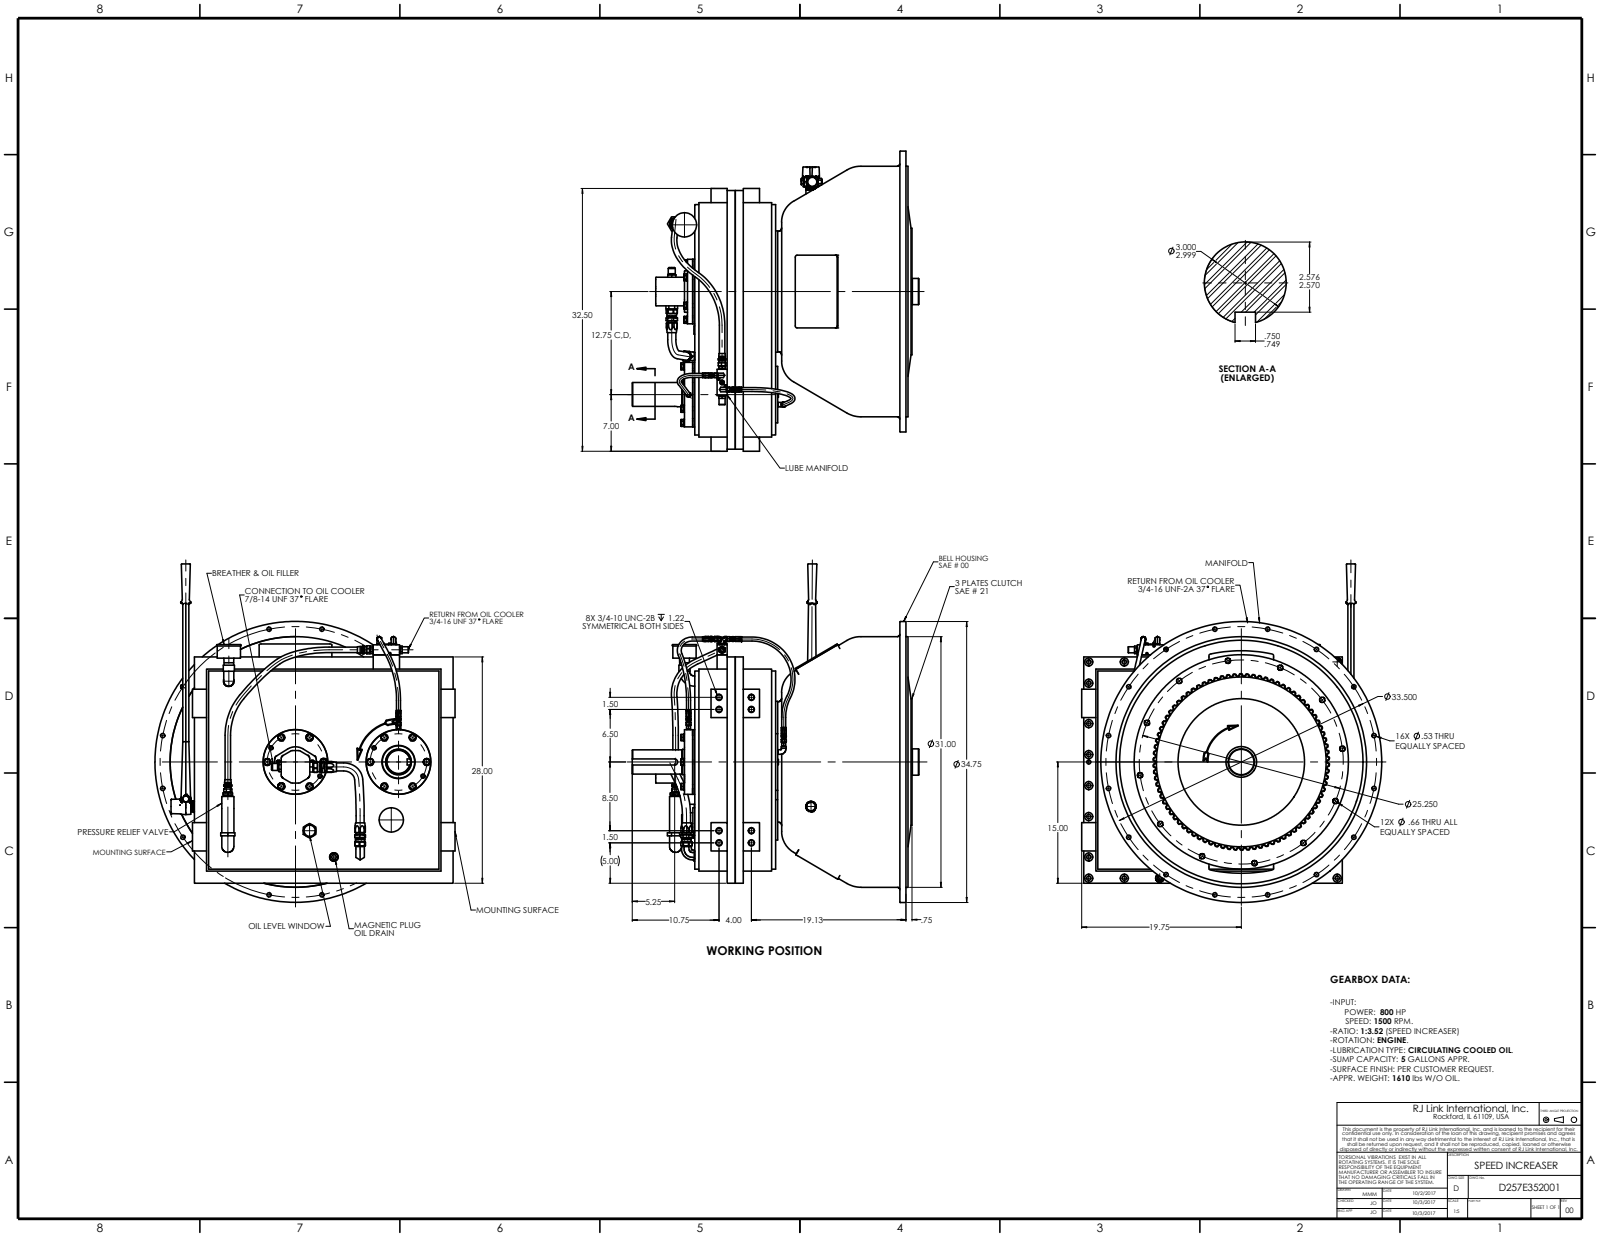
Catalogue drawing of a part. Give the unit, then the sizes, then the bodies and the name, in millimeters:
Units: millimetres
Overall size (bounding box): 1063.7 × 943 × 901.3
Round holes (diameter × count): ⌀13.5 ×70, ⌀25.4 ×34, ⌀16.7 ×20, ⌀12.9 ×12, ⌀16.7 ×12, ⌀5.2 ×6, ⌀6.4 ×6, ⌀16.2 ×6, ⌀11.1 ×5, ⌀3.2 ×4, ⌀4.4 ×4, ⌀4.4 ×4
Round bosses / shafts (diameter × count): ⌀19.1 ×22, ⌀12.7 ×18, ⌀15.9 ×16, ⌀22.2 ×12, ⌀15.1 ×8, ⌀27.4 ×6, ⌀23.8 ×6, ⌀23.8 ×6
Partial cylindrical surfaces — rounded edges, fillets, slot ends (radius × count): R1.5 ×36, R0.9 ×32, R3 ×27, R6.4 ×24, R1.3 ×15, R0.3 ×12, R0.4 ×12, R12.7 ×11
Main face-to-face distances: 12.7, 6.4, 241.3, 50.8, 127, 114.3, 19.1, 422.4, 38.1, 139.7
Hole centre spacings: 148.8, 165.1, 123.8, 251.1, 286, 111.6, 688.5, 38.1
Volume: 24 680 000 mm³ · Surface area: 9 374 000 mm²
Bodies: 72 solids, 4567 faces (1405 planar, 1763 cylindrical, 1399 other)
Part name (STEP PRODUCT): D257E352001; HA-12-12-12-14; OS3_125X4_003-2_2; LWZ_50_20 (+8 more)
STEP written by: SolidWorks 2017 (AUTOMOTIVE_DESIGN)
